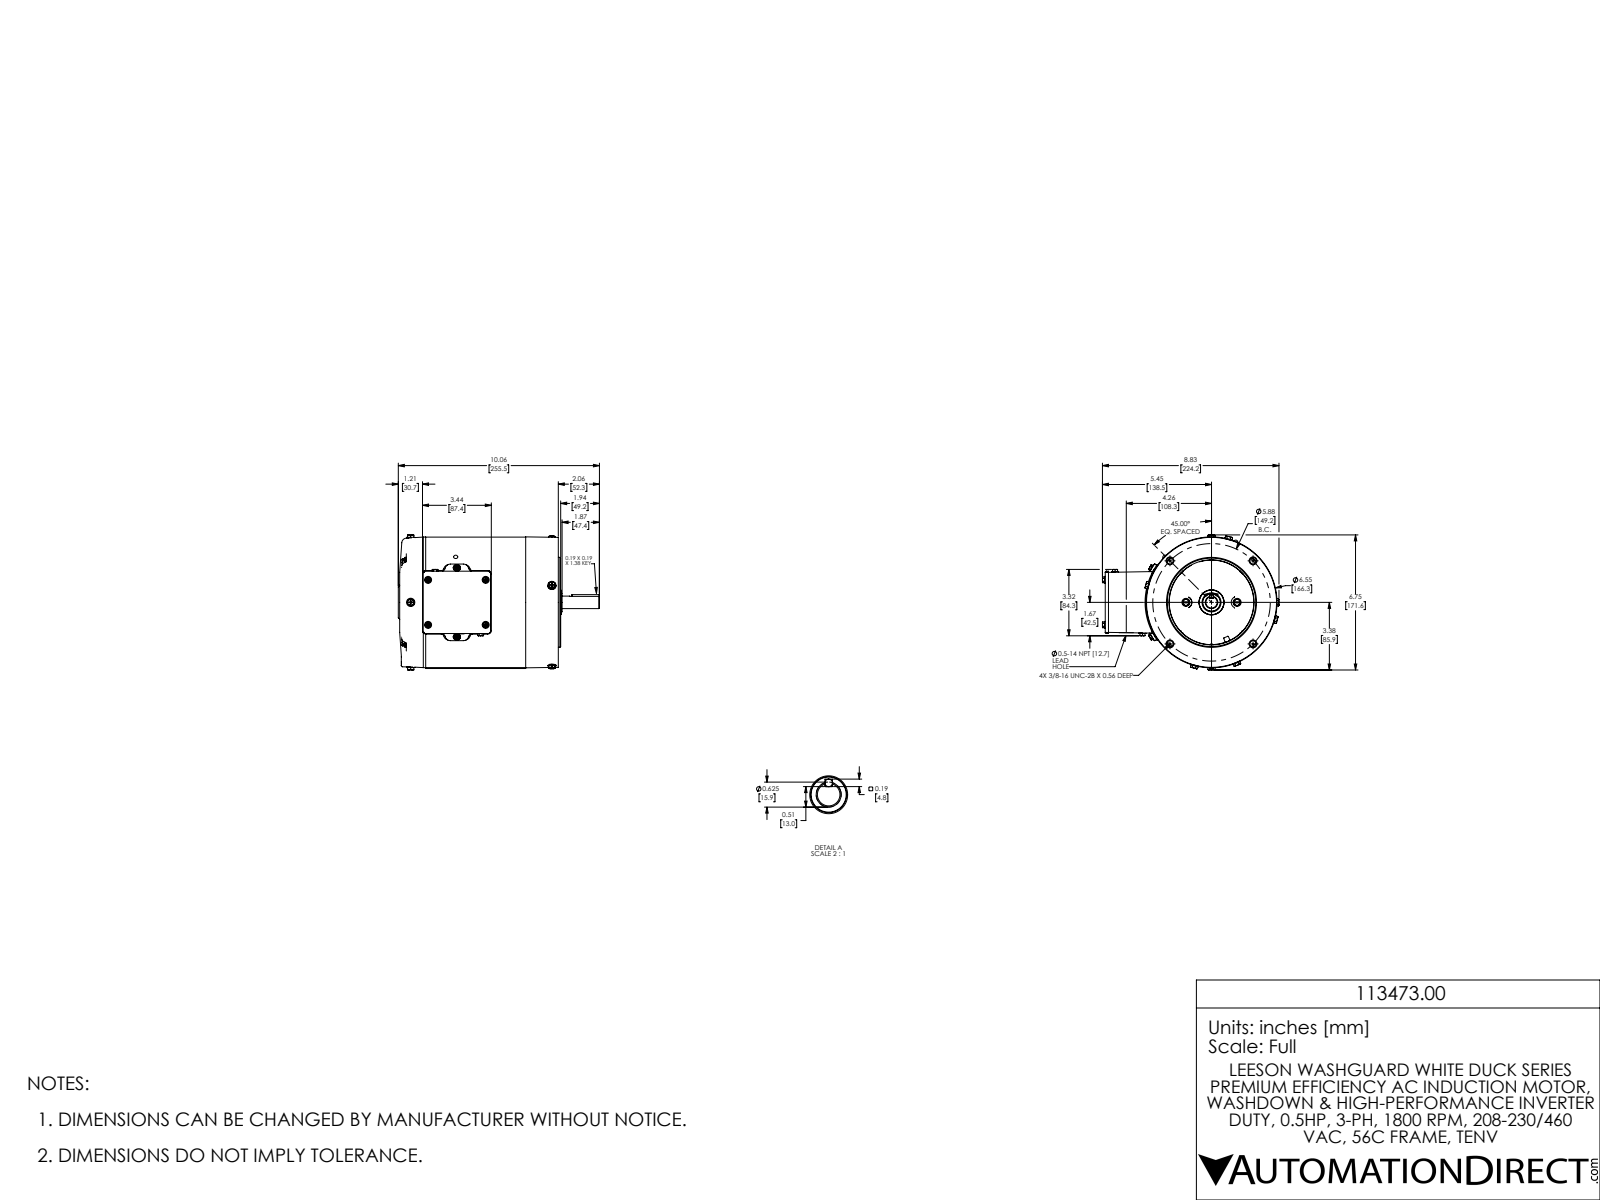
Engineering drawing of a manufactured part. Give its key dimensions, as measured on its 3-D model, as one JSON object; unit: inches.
{"part_name": "028834-500_Rev00_56C_0P5HP wo Front Bell COMPLETE A Coord", "step_written_by": "SolidWorks 2017 (AUTOMOTIVE_DESIGN)", "units": "inches", "bodies": {"solids": 43, "faces": 3765, "planar": 1130, "cylindrical": 543, "other": 2092}, "overall_size": [10.057, 8.827, 6.754], "volume_in3": 61.29, "surface_area_in2": 685.9, "round_holes": [[0.177, 7], [0.159, 4], [0.19, 4], [0.25, 4], [0.26, 4], [0.272, 4], [0.313, 4], [0.173, 3], [0.103, 2], [0.136, 2], [0.147, 2], [0.21, 2]], "round_bosses_or_shafts": [[0.19, 13], [0.348, 8], [0.164, 8], [0.414, 7], [0.399, 6], [0.5, 4], [0.166, 4], [0.112, 2]], "partial_cylinders_radius": [[0.06, 82], [0.03, 63], [0.13, 8], [0.25, 8], [0.005, 4], [0.025, 4], [0.053, 4], [0.09, 4]], "face_to_face_distances": [1.05, 0.048, 0.111, 0.063, 6.88, 7.93, 7.71, 0.83, 0.22, 0.12], "hole_center_spacings": [4.078, 0.11, 1.878, 2.095, 2.125, 2.193, 2.225, 2.828]}
